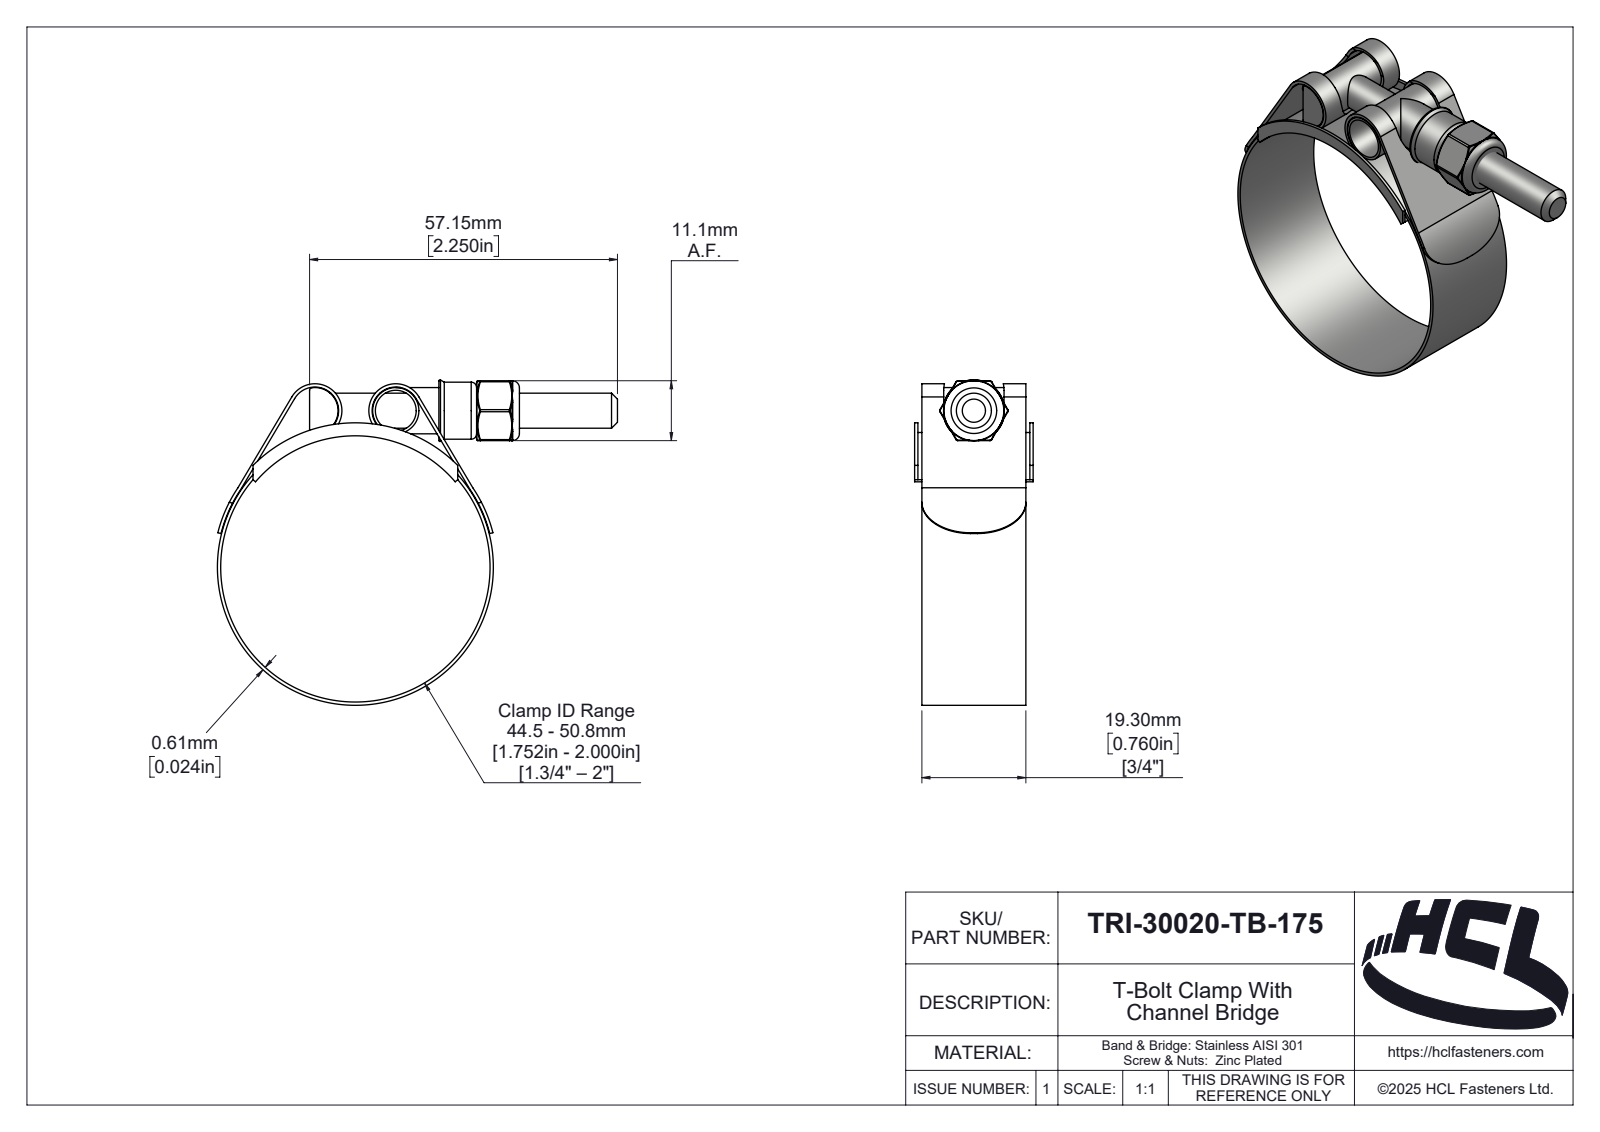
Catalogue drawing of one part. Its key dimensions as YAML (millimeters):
part_name: "TRI-30020-TB-175"
step_written_by: "SolidWorks 2025 (AUTOMOTIVE_DESIGN)"
units: millimeters
bodies: {solids: 6, faces: 338, planar: 48, cylindrical: 126, other: 164}
overall_size: [74.26, 60.38, 22]
volume: 6913
surface_area: 14867
round_holes:
  - {diameter: 5.4, count: 1}
  - {diameter: 6.35, count: 1}
  - {diameter: 6.5, count: 1}
  - {diameter: 7.58, count: 1}
  - {diameter: 50, count: 1}
round_bosses_or_shafts:
  - {diameter: 8.58, count: 2}
  - {diameter: 51.22, count: 1}
  - {diameter: 10.58, count: 1}
partial_cylinders:
  - {radius: 0.39, count: 6}
  - {radius: 0.5, count: 2}
  - {radius: 4.39, count: 2}
  - {radius: 5, count: 2}
  - {radius: 5.6, count: 2}
  - {radius: 0.59, count: 1}
  - {radius: 2.42, count: 1}
  - {radius: 3.03, count: 1}
face_to_face_distances: [0.61, 0.74, 1.35, 20.65, 19.3, 21.39, 20.04, 11.11, 22, 31]
hole_center_spacings: [30]
